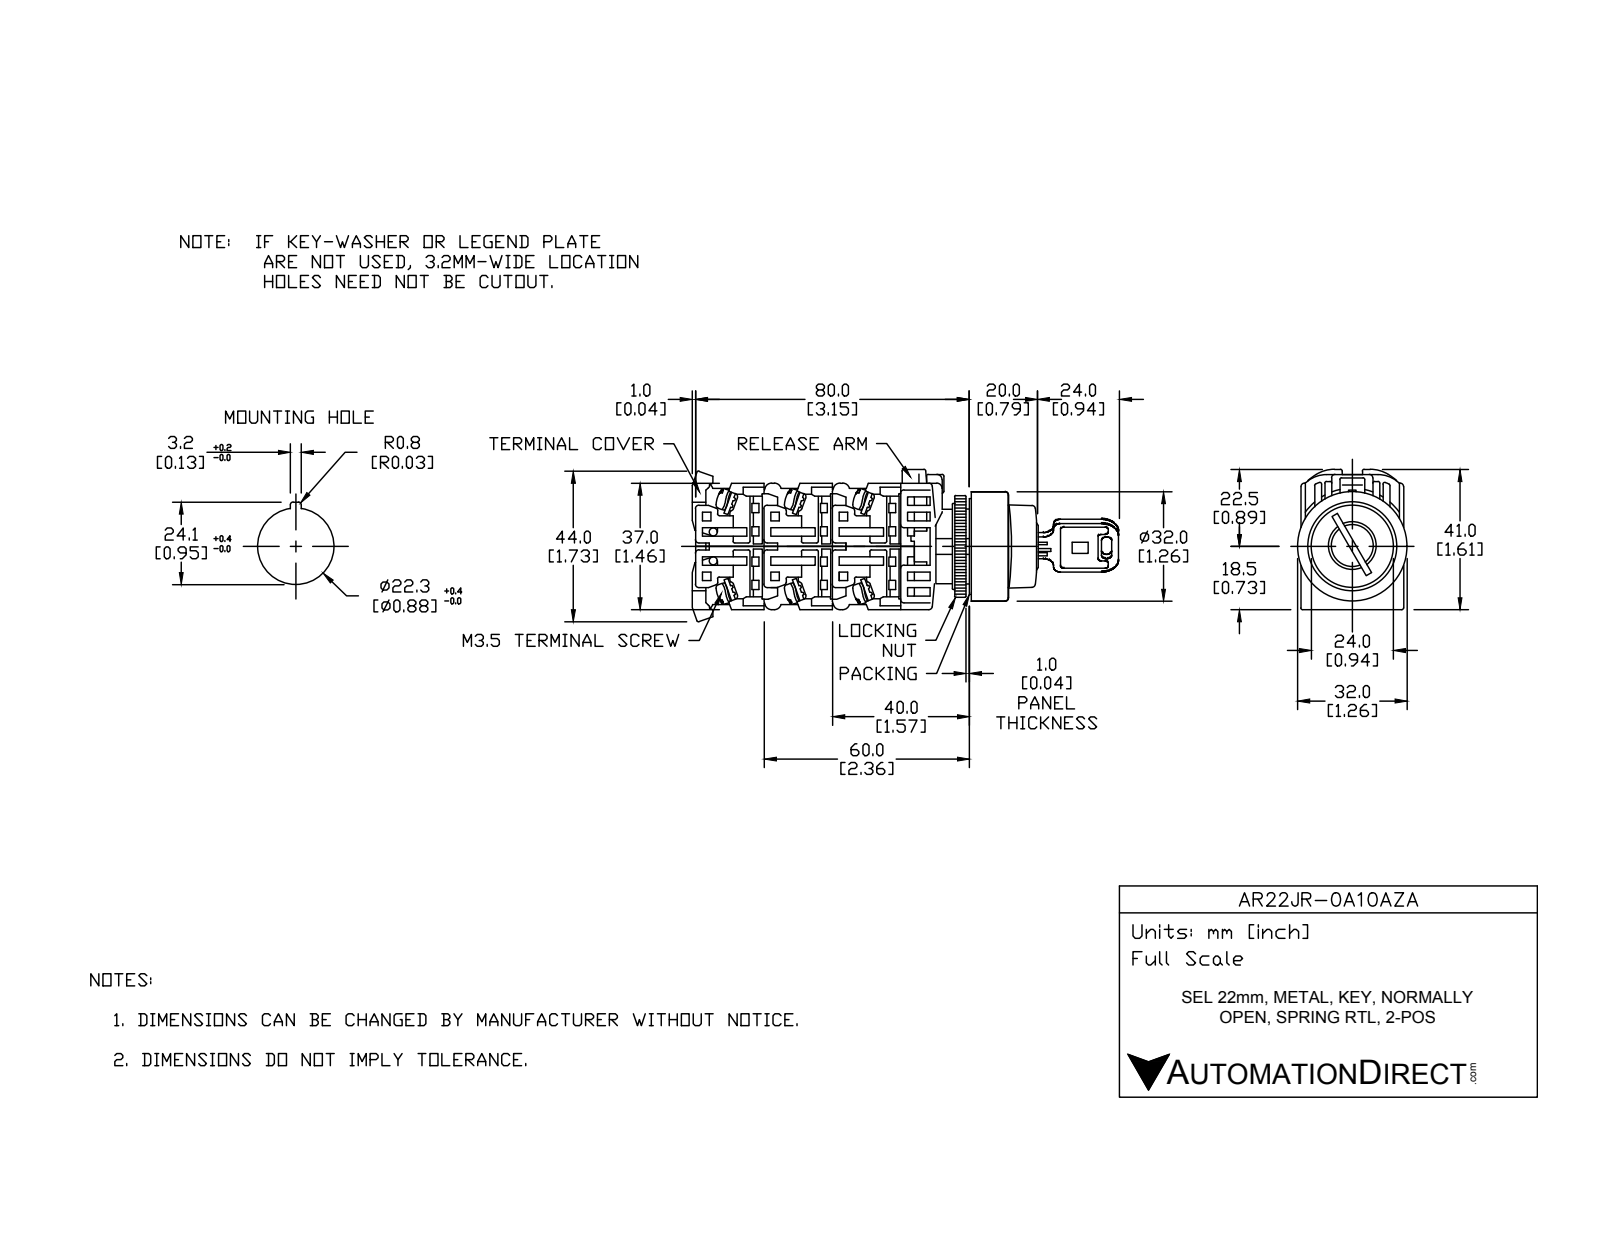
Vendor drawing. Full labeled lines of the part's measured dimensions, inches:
Part name (STEP PRODUCT): AR22JR-0A10AZA
STEP written by: SolidWorks 2017 (AUTOMOTIVE_DESIGN)
Units: inches
Bodies: 13 solids, 308 faces (208 planar, 78 cylindrical, 22 other)
Overall size (bounding box): 2.421 × 1.614 × 1.26
Volume: 1.892 in³ · Surface area: 32.95 in²
Round holes (diameter × count): ⌀0.551 ×1, ⌀0.858 ×1, ⌀0.866 ×1, ⌀0.984 ×1, ⌀1.22 ×1
Round bosses / shafts (diameter × count): ⌀0.197 ×2, ⌀1.26 ×1, ⌀1.201 ×1, ⌀1.173 ×1, ⌀0.945 ×1, ⌀0.856 ×1, ⌀0.669 ×1, ⌀0.543 ×1
Partial cylindrical surfaces — rounded edges, fillets, slot ends (radius × count): R0.02 ×23, R0.069 ×4, R0.197 ×4, R0.157 ×2, R0.653 ×1, R0.693 ×1
Main face-to-face distances: 0.039, 1.122, 0.787, 0.079, 0.709, 0.118, 1.142, 1.594, 0.906, 1.181
